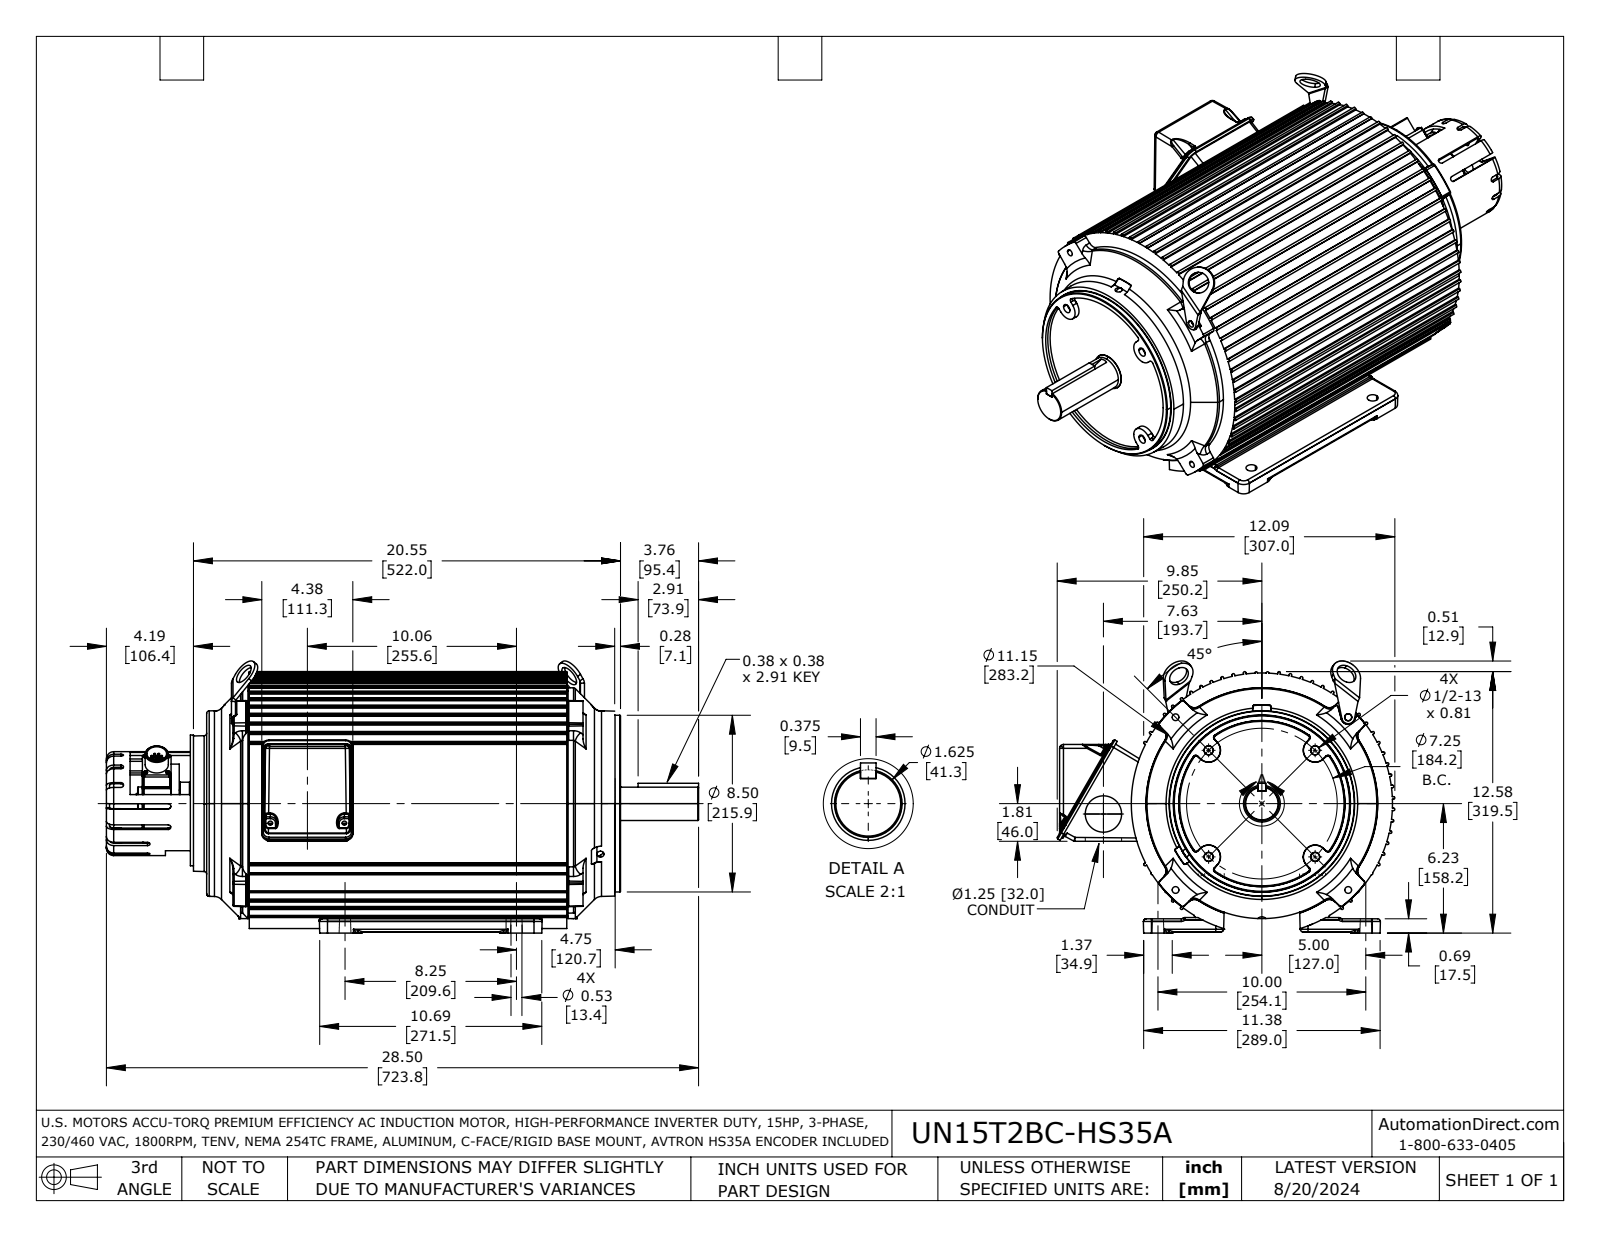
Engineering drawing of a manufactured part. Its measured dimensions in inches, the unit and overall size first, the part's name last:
Units: inches
Overall size (bounding box): 28.498 × 16.249 × 13.105
Round holes (diameter × count): ⌀0.4 ×6, ⌀0.12 ×4, ⌀0.2 ×4, ⌀0.313 ×4, ⌀0.328 ×4, ⌀0.344 ×4, ⌀0.136 ×3, ⌀1 ×3, ⌀0.107 ×2, ⌀1.75 ×2, ⌀0.945 ×1, ⌀1.387 ×1
Round bosses / shafts (diameter × count): ⌀0.072 ×8, ⌀0.175 ×4, ⌀0.12 ×4, ⌀0.15 ×3, ⌀0.072 ×2, ⌀10.847 ×1, ⌀8.5 ×1, ⌀5 ×1
Partial cylindrical surfaces — rounded edges, fillets, slot ends (radius × count): R0.063 ×115, R0.06 ×52, R0.125 ×51, R0.188 ×14, R0.219 ×8, R0.016 ×6, R0.25 ×6, R0.19 ×5
Main face-to-face distances: 0.125, 0.626, 21.371, 1.715, 19.656, 2.05, 19.045, 17.33, 2.326, 3.765
Hole centre spacings: 2.103, 2.937, 4.354, 4.8, 6.569, 7.219, 2.073, 2.234
Volume: 2 337 in³ · Surface area: 1 844 in²
Bodies: 24 solids, 2089 faces (585 planar, 635 cylindrical, 869 other)
Part name (STEP PRODUCT): UN15T2BC-HS35A
STEP written by: SolidWorks 2021 (AUTOMOTIVE_DESIGN)
